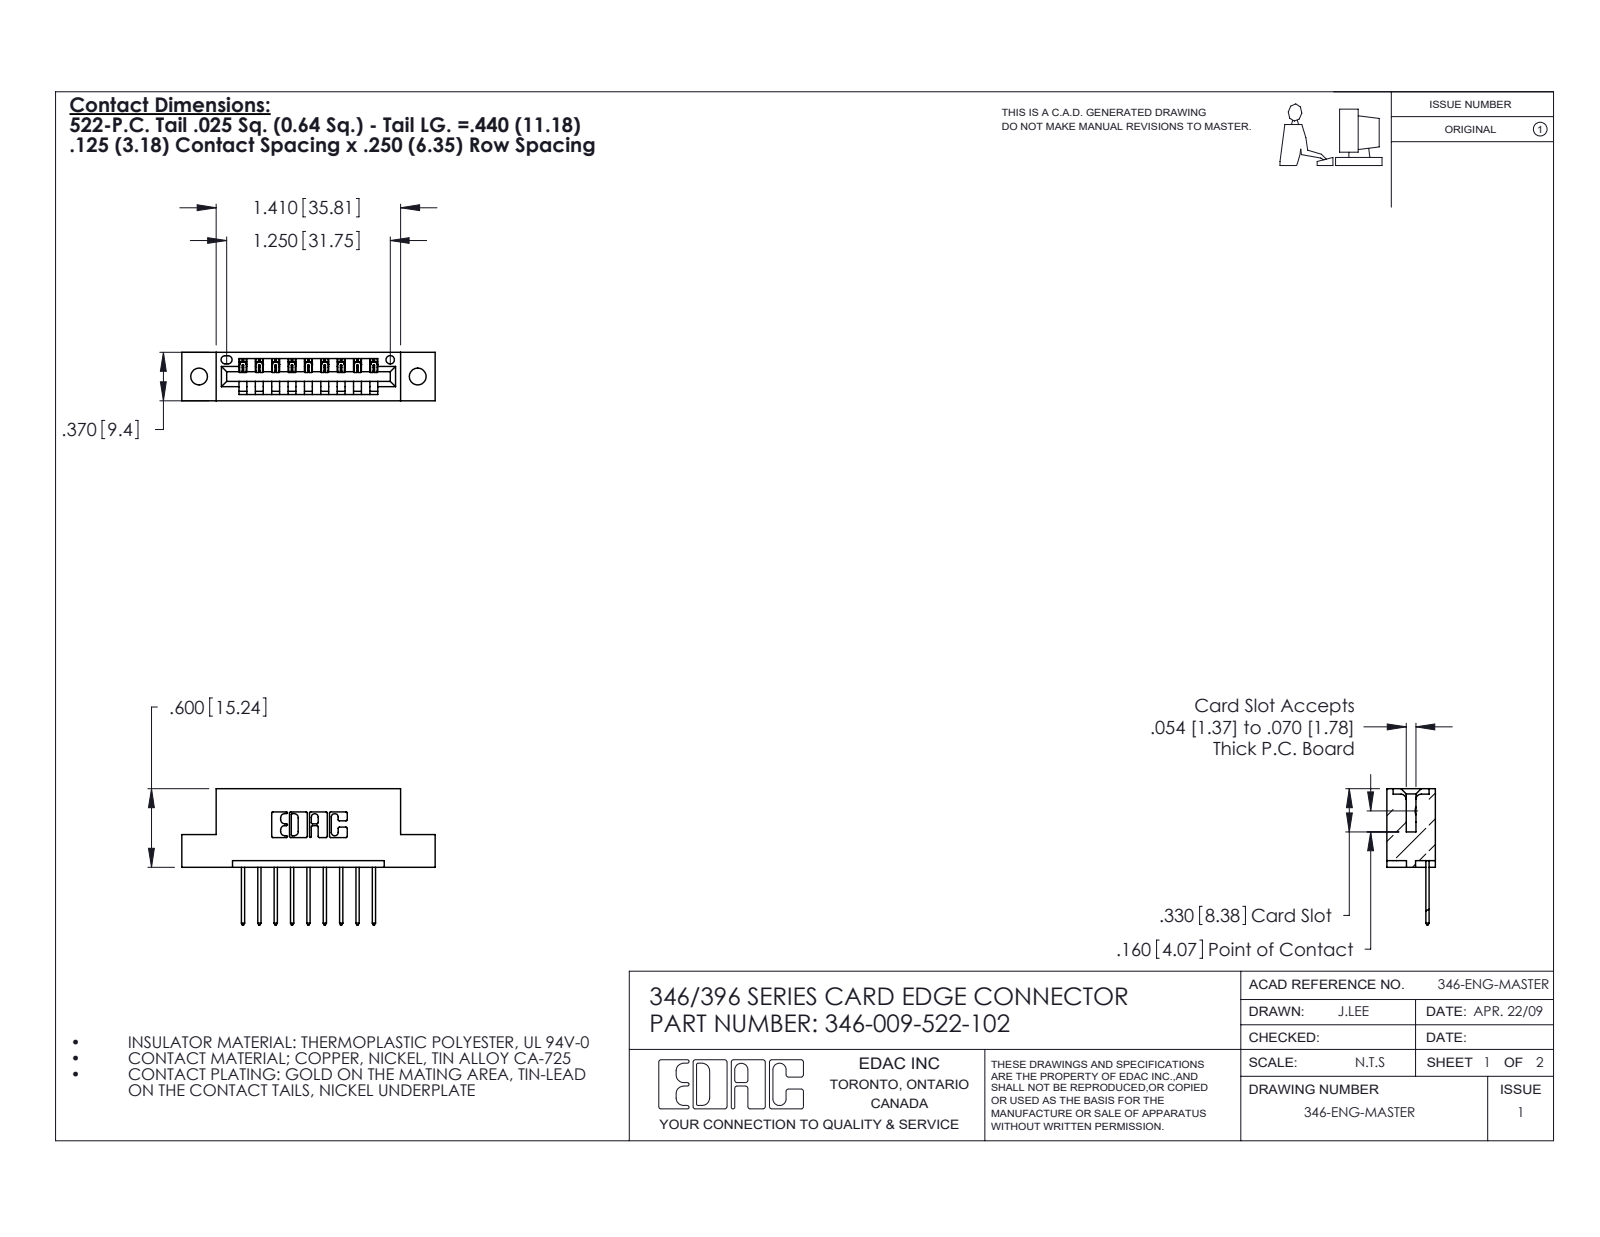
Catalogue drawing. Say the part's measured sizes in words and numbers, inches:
The part is named "345-292-001_345-293-122; 346-009-522-102; 346 Part_Flush Mounting Lugs - 0.128 Dia". Its 3-D file was written by "SolidWorks 2020 (CONFIG_CONTROL_DESIGN)". It is 10 solids with 644 faces: 436 planar, 208 cylindrical and 0 other. Overall it measures 1.935 by 1.04 by 0.37 inches. Its volume is 0.271 cubic inches and its surface area 7.684 square inches. Round holes: 2 of diameter 0.128, 1 of diameter 0.064. Partial cylindrical surfaces (rounded edges, fillets, slot ends): 22 of radius 0.01, 18 of radius 0.006, 18 of radius 0.01, 6 of radius 0.007, 6 of radius 0.031, 3 of radius 0.026, 2 of radius 0.031, 2 of radius 0.04. The main face-to-face distances are 0.25, 0.048, 0.322, 0.37, 0.072, 0.298, 0.025, 0.148, 0.222, 0.1. The hole center spacings are 0.246, 1.465, 1.67.
